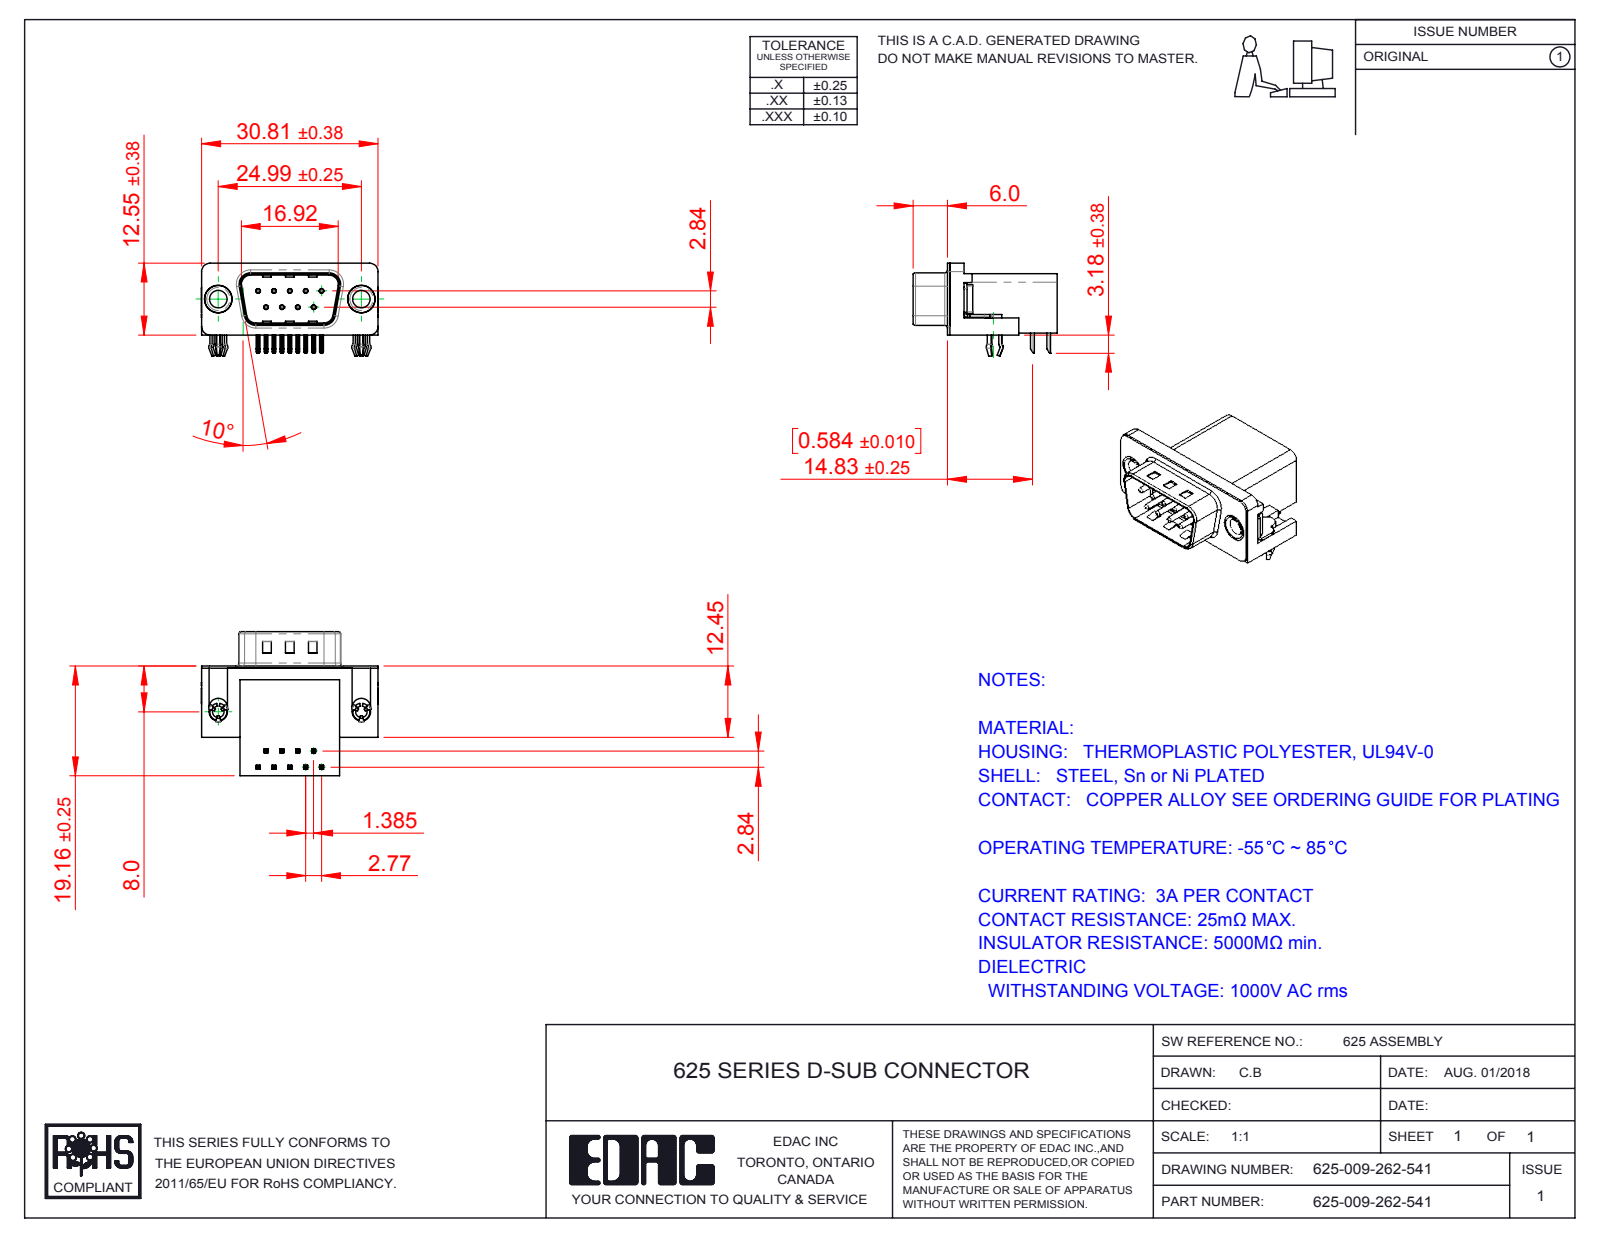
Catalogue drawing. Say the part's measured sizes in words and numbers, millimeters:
The part is named "625-009-262-541; 625 3 Prong Board Lock; 625 Shell_9 Socket; 625 Thru Hole Rivet (+3 more)". Its 3-D file was written by "SolidWorks 2016 (CONFIG_CONTROL_DESIGN)". It is 15 solids with 1057 faces: 611 planar, 305 cylindrical and 141 other. Overall it measures 30.89 by 25.16 by 16.25 millimeters. Its volume is 4 472 cubic millimeters and its surface area 4 989 square millimeters. Round holes: 9 of diameter 0.35, 9 of diameter 0.8, 2 of diameter 2, 2 of diameter 3.05, 2 of diameter 4, 2 of diameter 4.8, 2 of diameter 5. Round bosses or shafts: 9 of diameter 0.75, 2 of diameter 4.9, 2 of diameter 4.75, 2 of diameter 3.85, 2 of diameter 3. Partial cylindrical surfaces (rounded edges, fillets, slot ends): 48 of radius 0.25, 18 of radius 0.12, 16 of radius 1, 9 of radius 0.5, 8 of radius 1.5, 8 of radius 1.6, 4 of radius 0.9, 4 of radius 2. The main face-to-face distances are 0.4, 10.34, 18.76, 19.16, 2.9, 16.26, 2.5, 0.35, 10.69, 6.7. The hole center spacings are 3.16, 2.77, 5.54, 5.03, 5.04, 8.31, 7.48, 7.49.
